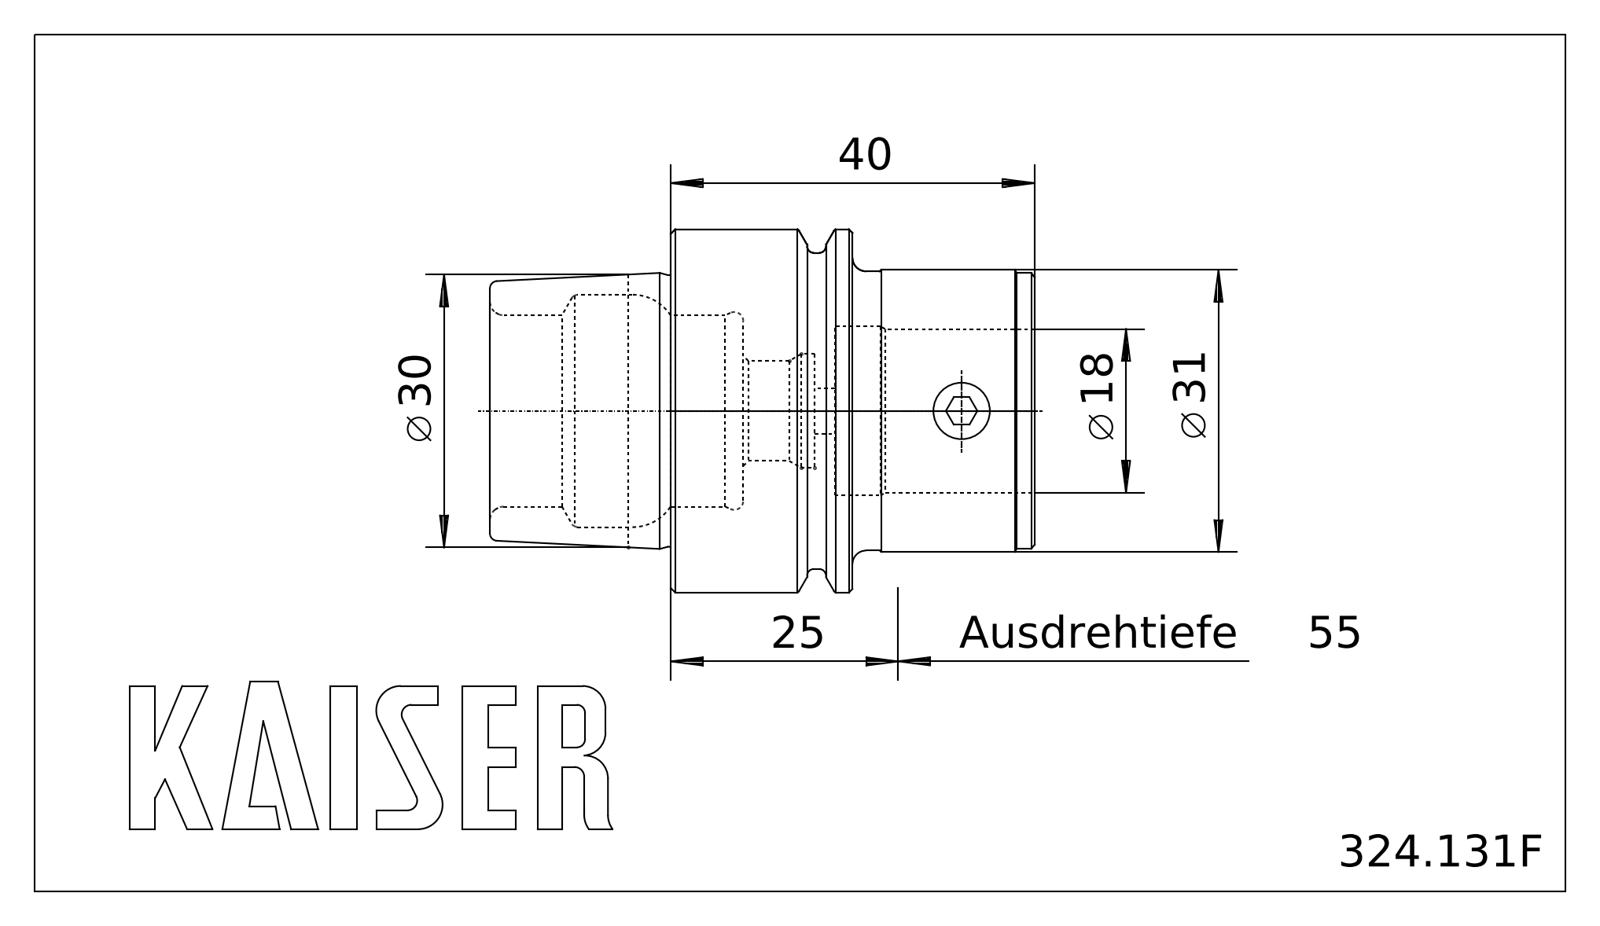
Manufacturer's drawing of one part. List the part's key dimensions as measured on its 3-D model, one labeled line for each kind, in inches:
Part name (STEP PRODUCT): 324.131F Kaiser HSK-E40xCK3x55|690.433 Kaiser ETL M6 X 8,5 CK3;Schnitt-Linear austragen2; 324.131F Kaiser HSK-E40xCK3x55|324.131F Kaiser HSK-E40xCK3x55;Schnitt-Rotation3
STEP written by: ACIS (automotive_design)
Units: inches
Bodies: 2 solids, 149 faces (33 planar, 36 cylindrical, 80 other)
Overall size (bounding box): 2.358 × 1.573 × 1.573
Volume: 2.103 in³ · Surface area: 19.99 in²
Round holes (diameter × count): ⌀0.197 ×1, ⌀0.212 ×1, ⌀0.244 ×1, ⌀0.433 ×1, ⌀0.492 ×1, ⌀0.709 ×1, ⌀0.728 ×1, ⌀0.828 ×1, ⌀1.006 ×1
Round bosses / shafts (diameter × count): ⌀1.573 ×1, ⌀1.368 ×1, ⌀1.22 ×1, ⌀1.209 ×1, ⌀1.193 ×1, ⌀0.236 ×1
Partial cylindrical surfaces — rounded edges, fillets, slot ends (radius × count): R0.108 ×2
Main face-to-face distances: 1.575, 0.789, 0.785, 0.866, 0.077, 0.709, 1.262, 0.472, 0.396, 0.313
